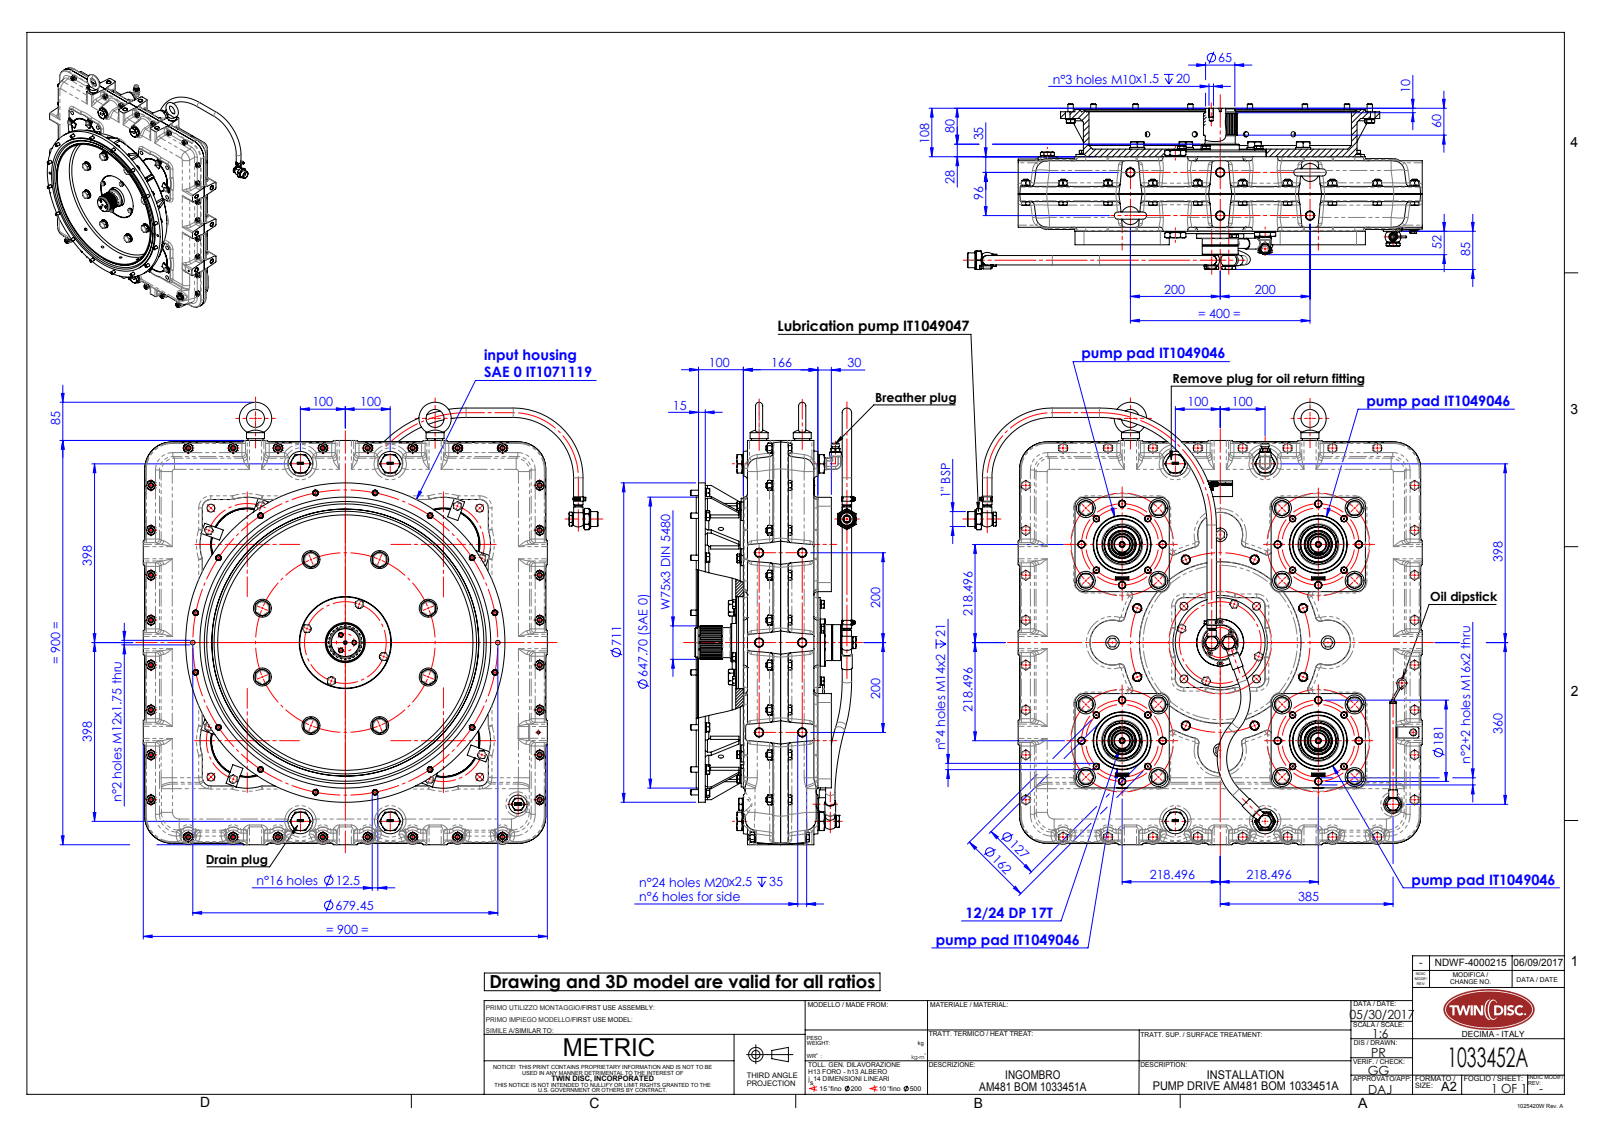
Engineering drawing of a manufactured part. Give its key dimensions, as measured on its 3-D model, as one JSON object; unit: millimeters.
{"part_name": "1033452A; IT1049047_rev00-installation; IT1049046_rev00-installation; IT1071119_rev00-installation (+7 more)", "step_written_by": "SolidWorks 2015 (AUTOMOTIVE_DESIGN)", "units": "millimeters", "bodies": {"solids": 329, "faces": 14390, "planar": 6389, "cylindrical": 4456, "other": 3545}, "overall_size": [1013, 985, 369], "volume_mm3": 116200000, "surface_area_mm2": 9007000, "round_holes": [[12.2, 56], [13, 51], [8.5, 43], [17.5, 40], [10.3, 36], [21, 34], [14, 32], [20.2, 26], [12, 24], [11, 22], [10.2, 18], [12.5, 16]], "round_bosses_or_shafts": [[21.1, 56], [18, 56], [12, 52], [33.6, 26], [20, 26], [29, 24], [10, 23], [18.1, 16]], "partial_cylinders_radius": [[0.35, 346], [38.33, 288], [8, 150], [20, 64], [29.53, 58], [10.97, 36], [5, 32], [19, 32]], "face_to_face_distances": [83, 9, 157, 74, 100, 166, 17, 183, 148, 26], "hole_center_spacings": [200, 94.38, 100, 145.91, 219.56, 221.85, 246.7, 282.85]}
